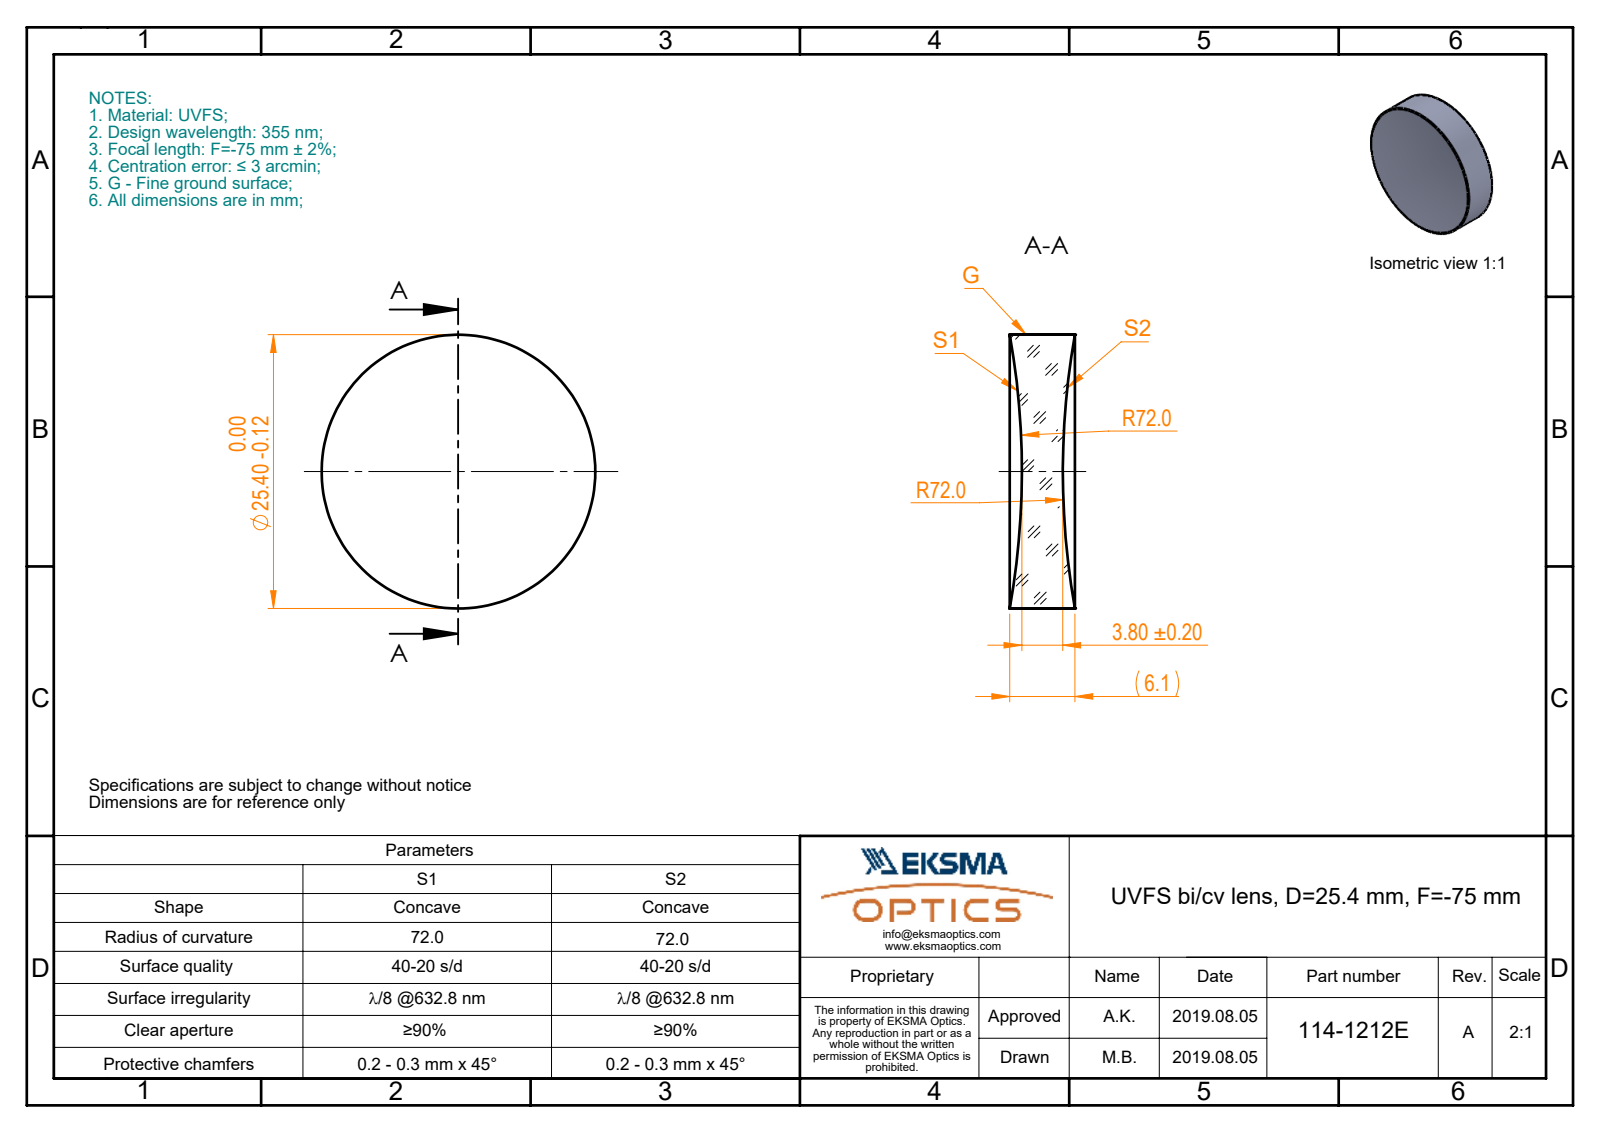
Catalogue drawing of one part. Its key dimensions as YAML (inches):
part_name: "114-1212E UVFS bi-cv 25.4 F-75"
step_written_by: "SolidWorks 2017 (CONFIG_CONTROL_DESIGN)"
units: inches
bodies: {solids: 1, faces: 6, planar: 0, cylindrical: 2, other: 4}
overall_size: [1, 1, 0.239]
volume: 0.152
surface_area: 2.333
round_bosses_or_shafts:
  - {diameter: 1, count: 1}
